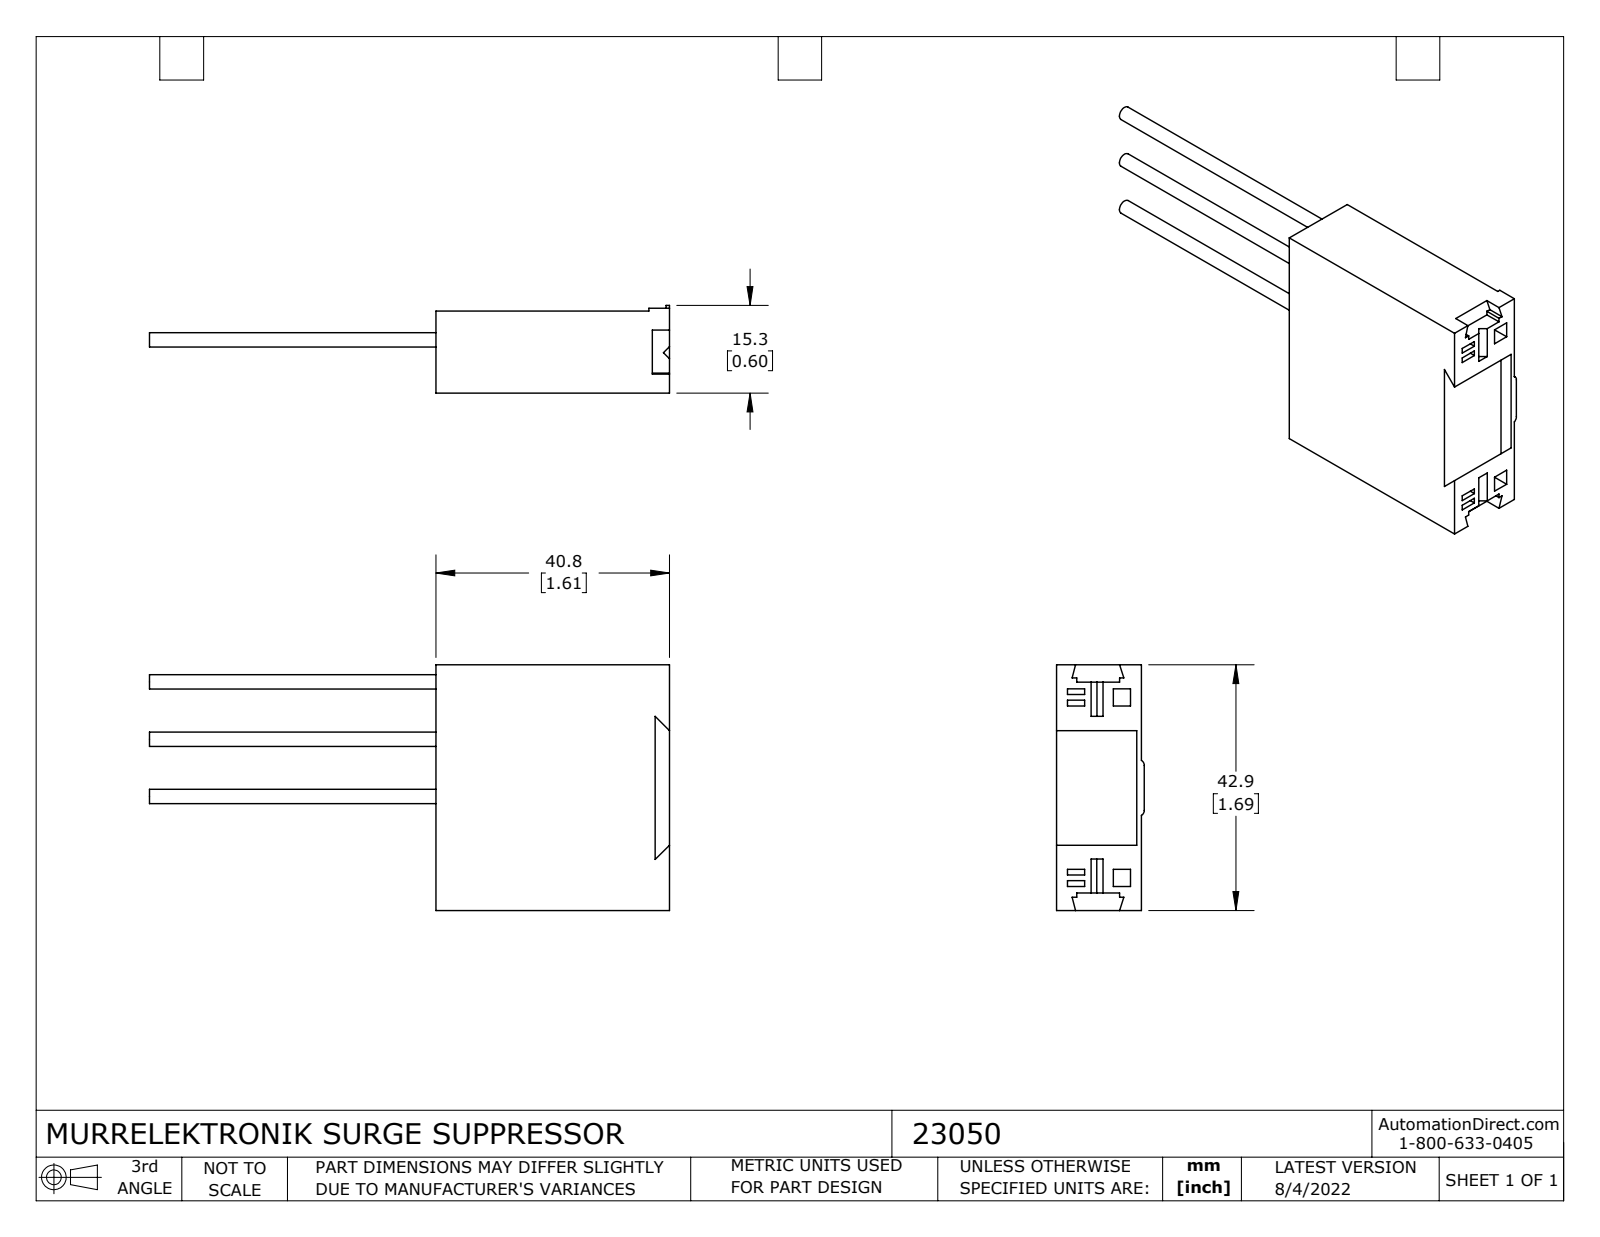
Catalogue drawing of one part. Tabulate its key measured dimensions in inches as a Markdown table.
| quantity | value |
| --- | --- |
| part name | 23050 |
| STEP written by | SolidWorks 2021 (CONFIG_CONTROL_DESIGN) |
| units | inches |
| bodies | 1 solid, 77 faces (69 planar, 6 cylindrical, 2 other) |
| overall size | 3.575 × 1.689 × 0.602 |
| volume | 1.514 in³ |
| surface area | 11.66 in² |
| round bosses / shafts (diameter × count) | 0.098 × 3 |
| main face-to-face distances | 0.563, 1.689, 1.508, 1.606, 0.098, 0.02, 0.118, 0.583, 1.488, 0.039 |
